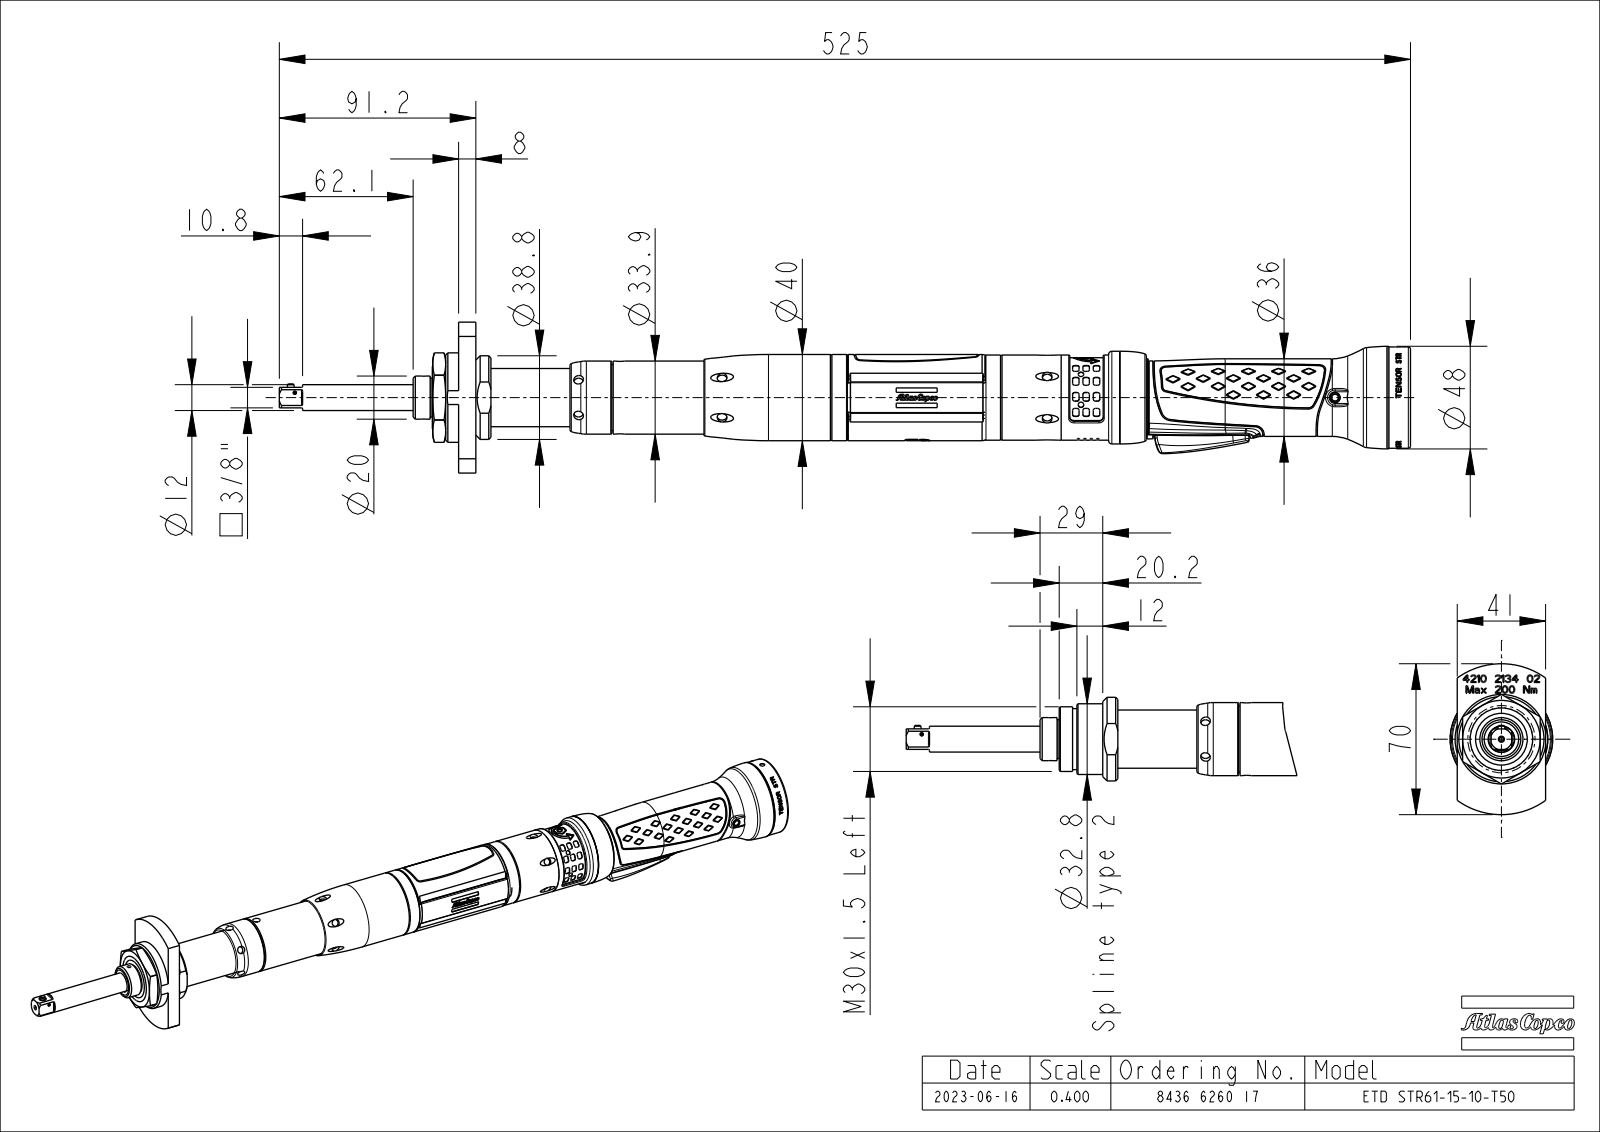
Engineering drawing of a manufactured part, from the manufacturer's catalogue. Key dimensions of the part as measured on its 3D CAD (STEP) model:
Part name (STEP PRODUCT): FRONT_SW0001; HANDLE_SW0002; 4220524500; 4220524501 (+1 more)
STEP written by: CREO PARAMETRIC BY PTC INC, 2022414 (CONFIG_CONTROL_DESIGN)
Units: millimetres
Bodies: 4 solids, 3989 faces (1754 planar, 550 cylindrical, 1685 other)
Overall size (bounding box): 524.93 × 70 × 47.62
Volume: 529 686 mm³ · Surface area: 82 836 mm²
Round holes (diameter × count): ⌀4.5 ×10, ⌀3.2 ×2, ⌀0.38 ×1, ⌀0.7 ×1, ⌀1.5 ×1, ⌀1.9 ×1, ⌀2.2 ×1, ⌀3 ×1, ⌀4.7 ×1, ⌀5 ×1, ⌀40.8 ×1
Round bosses / shafts (diameter × count): ⌀47 ×1, ⌀43 ×1, ⌀41.5 ×1, ⌀40 ×1, ⌀39.6 ×1, ⌀39.5 ×1, ⌀39.4 ×1, ⌀39.36 ×1
Partial cylindrical surfaces — rounded edges, fillets, slot ends (radius × count): R0.2 ×26, R0.5 ×21, R0.3 ×12, R3 ×12, R2 ×7, R0.4 ×4, R0.6 ×4, R0.8 ×4
Main face-to-face distances: 433.73, 12.2, 319.13, 8, 441.73, 311.13, 134.8, 298.93, 306.93, 261.85
Hole centre spacings: 66.1, 151.35, 217.45, 5.07, 6.08, 11.1, 19.15, 46.95
